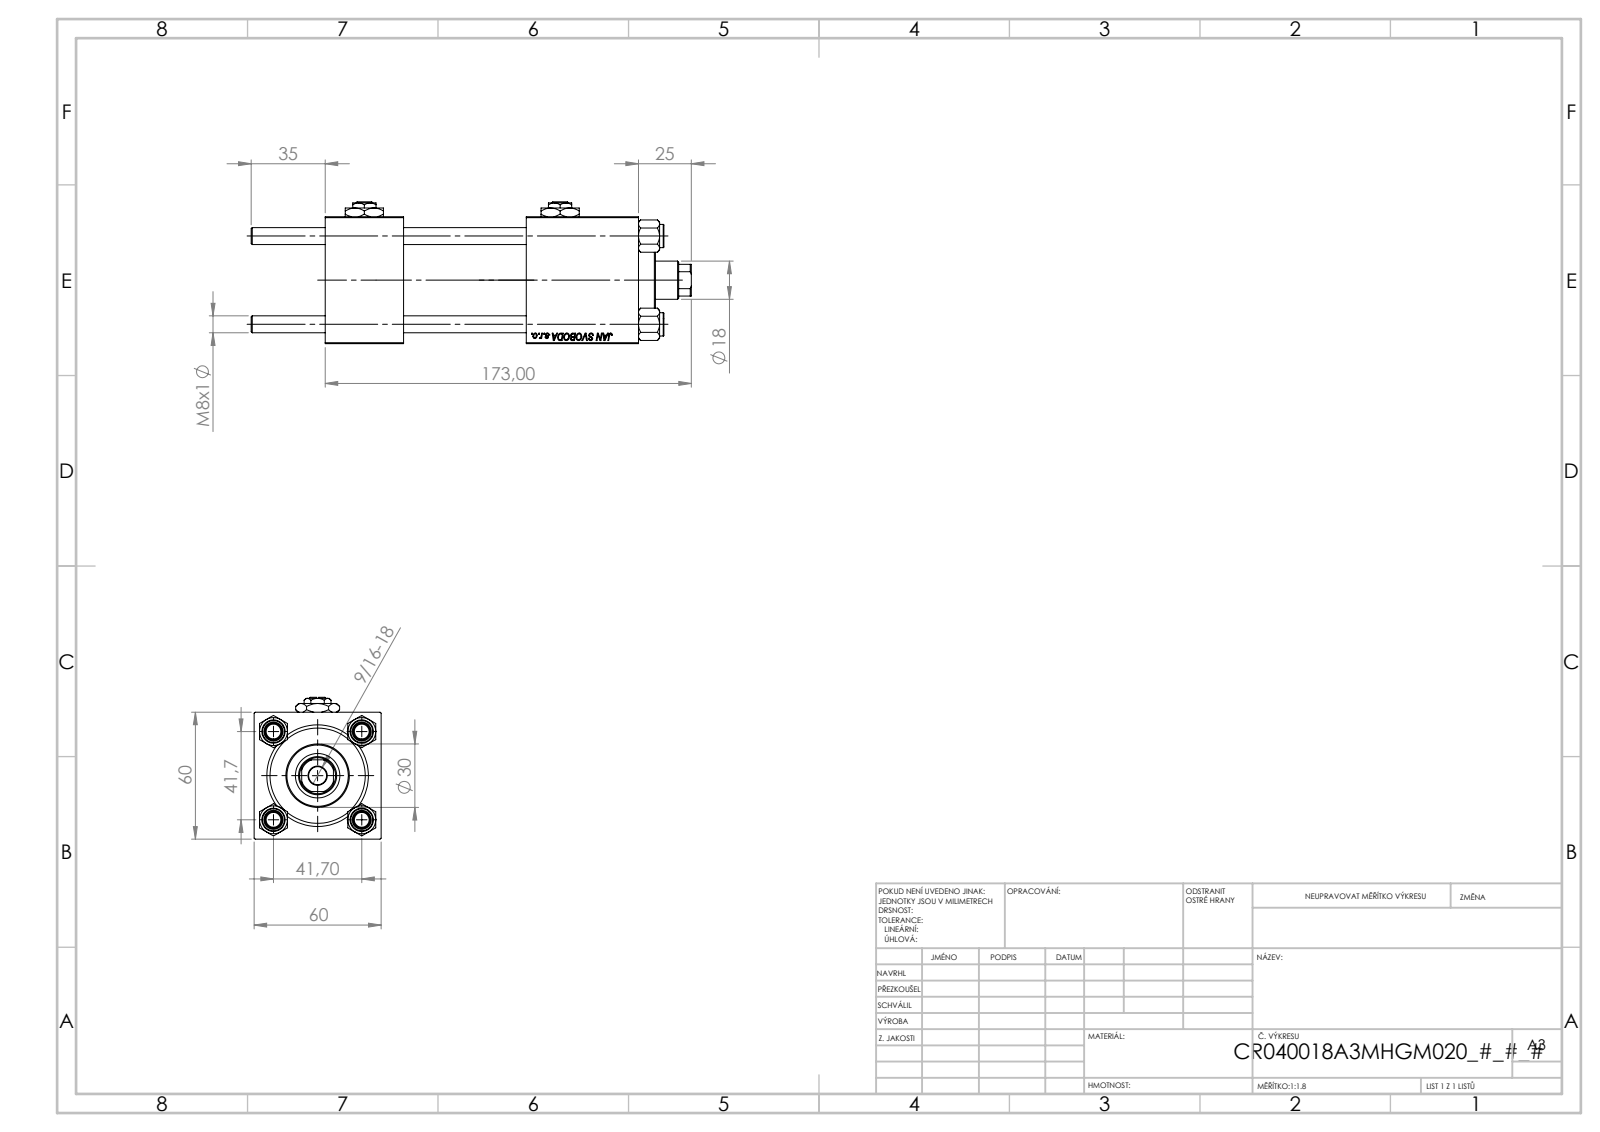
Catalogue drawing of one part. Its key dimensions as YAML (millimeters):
part_name: "CR025_012_A_0_G_A_G_M_020_+#_##_TYCINKA; V215CR_VCP; NUT_M5; V215_VC_A (+2 more)"
step_written_by: "SolidWorks 2019 (CONFIG_CONTROL_DESIGN)"
units: millimeters
bodies: {solids: 13, faces: 1235, planar: 569, cylindrical: 88, other: 578}
overall_size: [208, 67, 60]
volume: 410653
surface_area: 116925
round_holes:
  - {diameter: 8, count: 4}
  - {diameter: 7, count: 2}
  - {diameter: 16.66, count: 2}
  - {diameter: 24, count: 2}
  - {diameter: 8.5, count: 1}
  - {diameter: 18, count: 1}
  - {diameter: 21, count: 1}
  - {diameter: 31, count: 1}
  - {diameter: 40, count: 1}
  - {diameter: 45, count: 1}
round_bosses_or_shafts:
  - {diameter: 11, count: 4}
  - {diameter: 46, count: 1}
  - {diameter: 30, count: 1}
partial_cylinders:
  - {radius: 8.5, count: 1}
face_to_face_distances: [60, 37, 148, 111, 58, 53, 95, 119.3, 82.3, 24.3]
hole_center_spacings: [29.49, 41.7, 58.97, 92.5]
